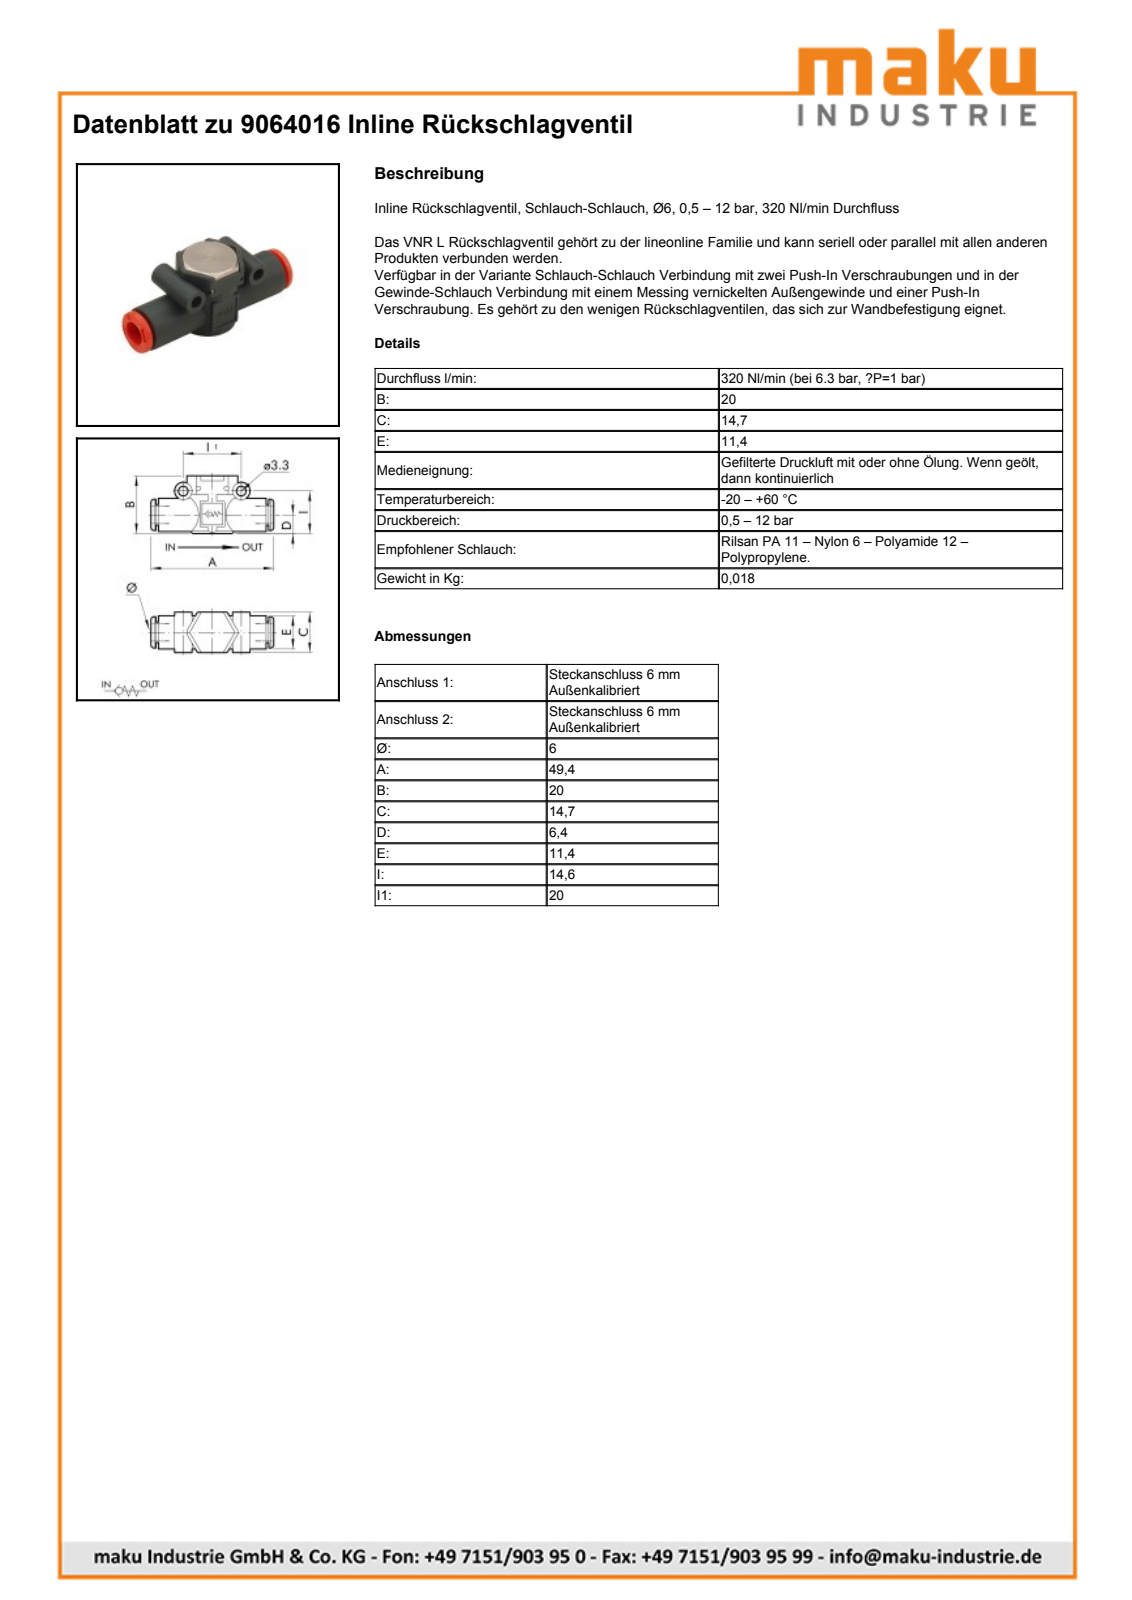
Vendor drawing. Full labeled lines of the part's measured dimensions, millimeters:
Part name (STEP PRODUCT): 9064016; LINE-ON-LINE D6 VSR-L body; LINE-ON-LINE D6 VNR-L bushing; LINE ON LINE D6 VNR-L plate
STEP written by: PARTsolutions (AUTOMOTIVE_DESIGN)
Units: millimetres
Bodies: 4 solids, 144 faces (91 planar, 46 cylindrical, 7 other)
Overall size (bounding box): 49 × 20 × 14.7
Volume: 4 065 mm³ · Surface area: 6 394 mm²
Round holes (diameter × count): ⌀3.3 ×2, ⌀3.5 ×1, ⌀4 ×1, ⌀6 ×1, ⌀6.2 ×1, ⌀7.4 ×1, ⌀9 ×1, ⌀9.6 ×1, ⌀10.3 ×1, ⌀11.6 ×1
Round bosses / shafts (diameter × count): ⌀6 ×2, ⌀14.8 ×1, ⌀11.4 ×1, ⌀11 ×1, ⌀7.6 ×1, ⌀7.2 ×1
Partial cylindrical surfaces — rounded edges, fillets, slot ends (radius × count): R3.75 ×1, R7.9 ×1, R7.95 ×1, R9.15 ×1
Main face-to-face distances: 1.6, 1.04, 40.96, 18.4, 20, 13.9, 1.4, 1.8, 2.84, 42.76
Hole centre spacings: 12.74, 20
